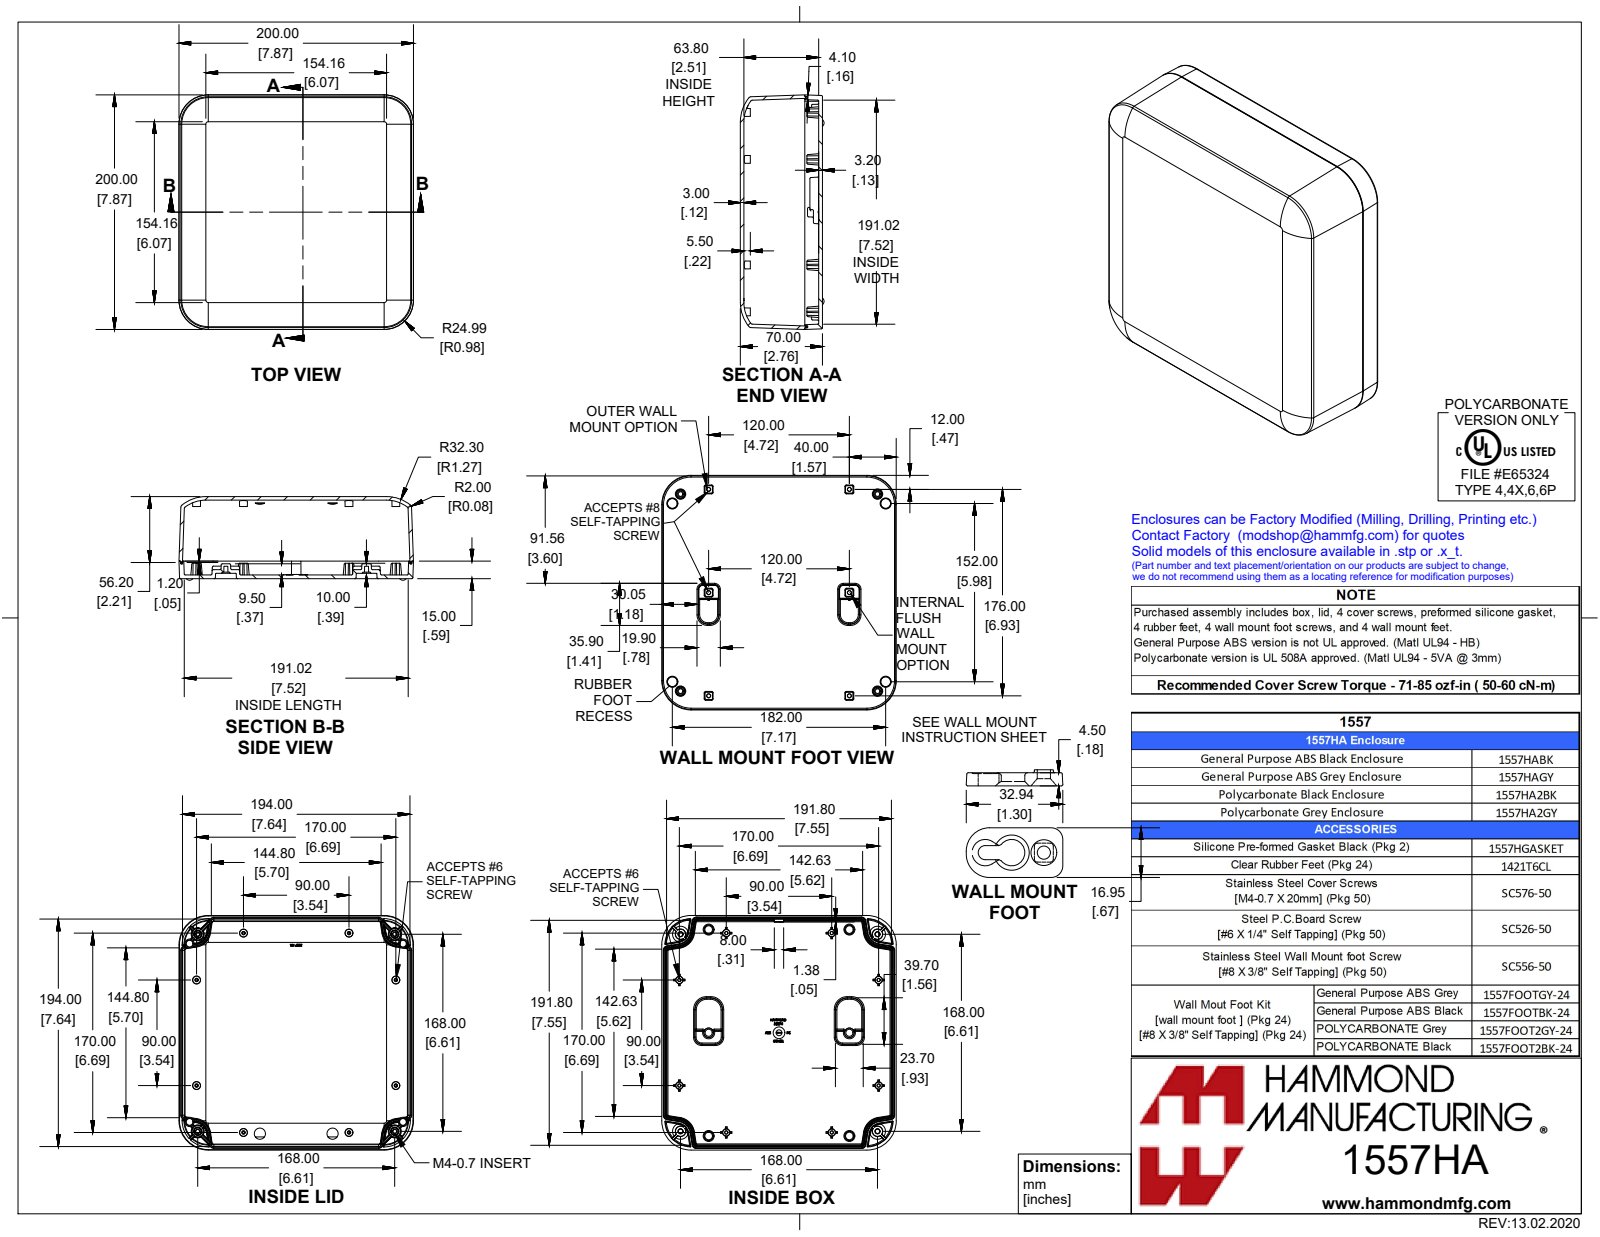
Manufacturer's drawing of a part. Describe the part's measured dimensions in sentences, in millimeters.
The part is named "(screw #8X 3_8''''''''FH Self-tap plastite); SC576 (screw M4-0.7X 20mm PN); PFR1421T4; IN-M4 (insert M4-0.7X5.75mm SS) KNURLS (+5 more)". Its 3-D file was written by "SolidWorks 2019 (CONFIG_CONTROL_DESIGN)". It is 23 solids with 2923 faces: 978 planar, 570 cylindrical and 1375 other. Overall it measures 229 by 200 by 74.5 millimeters. Its volume is 438 500 cubic millimeters and its surface area 304 100 square millimeters. Round holes: 4 of diameter 3.3, 4 of diameter 4.5. Round bosses or shafts: 12 of diameter 1.8, 4 of diameter 8, 4 of diameter 7.7, 4 of diameter 6.4, 4 of diameter 5.5, 4 of diameter 5.3, 4 of diameter 4.2, 4 of diameter 3.9. Partial cylindrical surfaces (rounded edges, fillets, slot ends): 101 of radius 0.5, 78 of radius 1, 12 of radius 4, 8 of radius 0.2, 8 of radius 0.3, 8 of radius 0.4, 8 of radius 1.5, 8 of radius 2.1. The main face-to-face distances are 3, 3.2, 67, 63.8, 70, 66.8, 196.8, 199.8, 3, 4.1. The hole center spacings are 24.3, 144.1, 168, 173.7, 224.3, 120, 176, 213.
